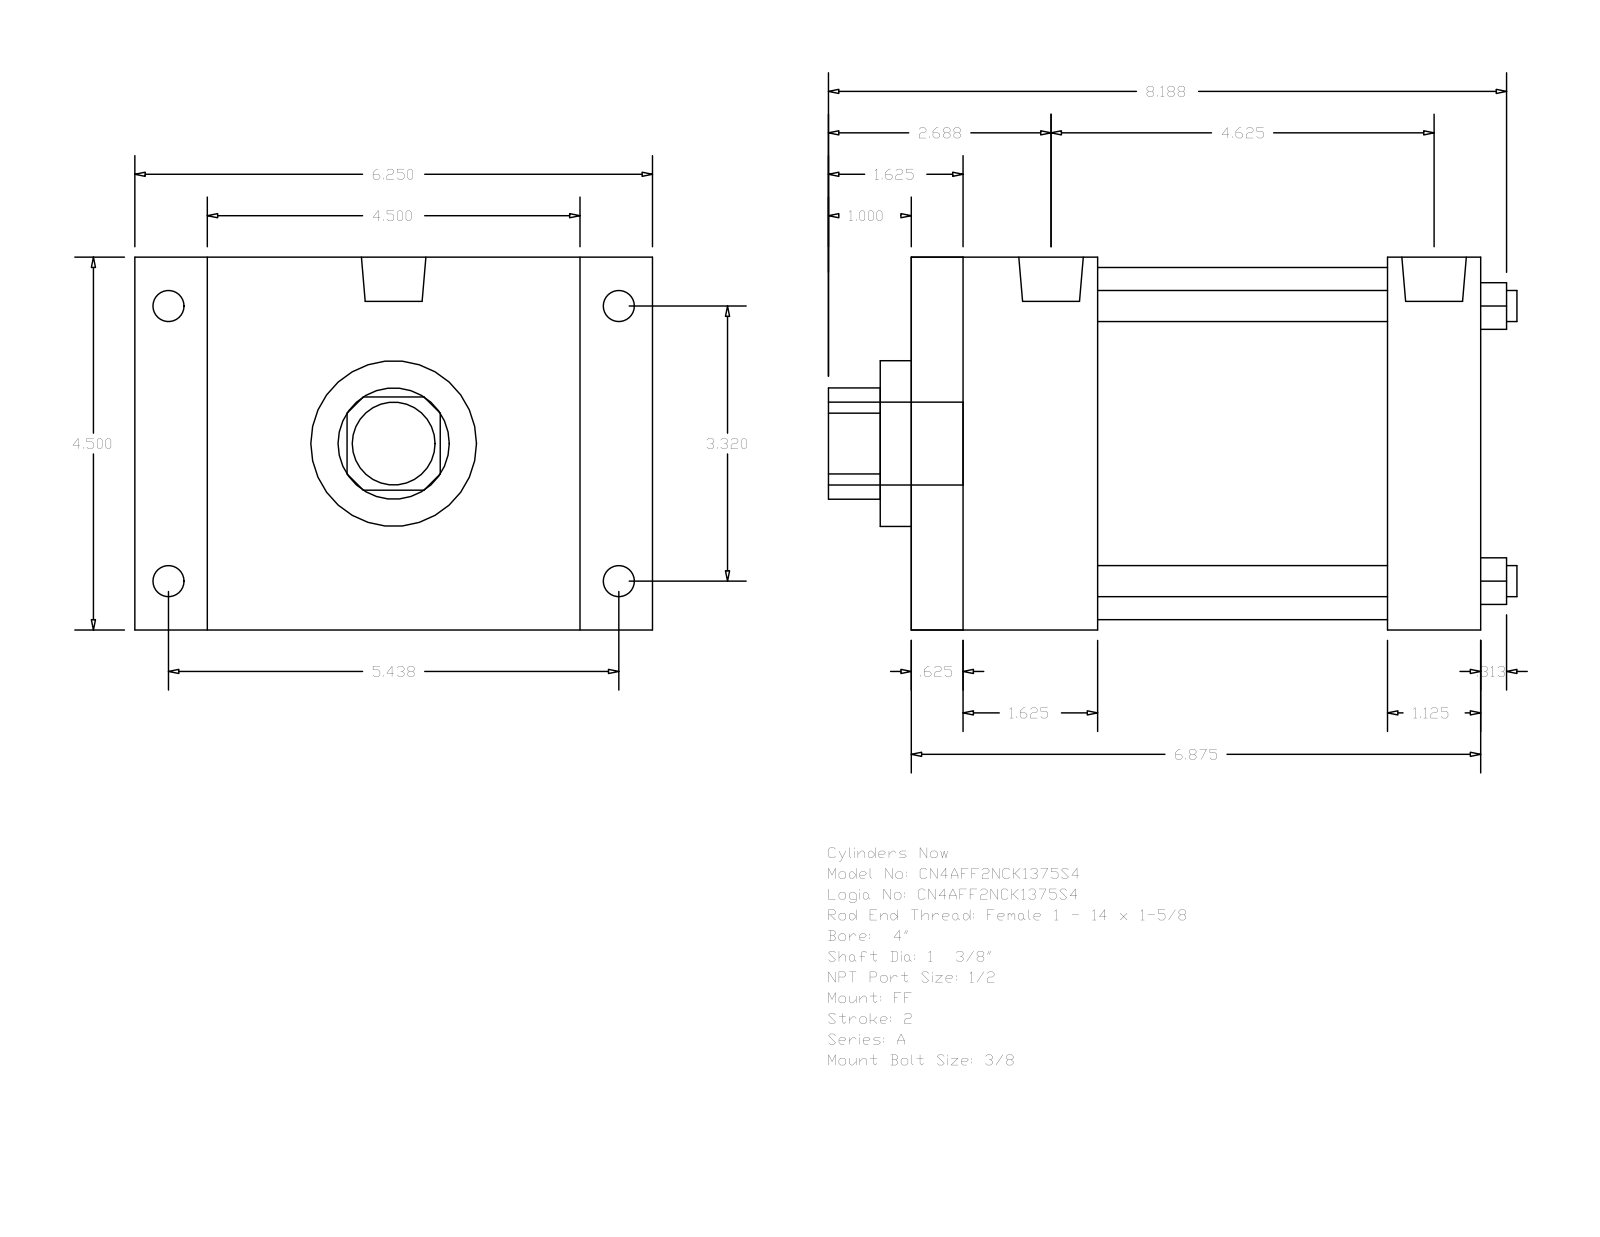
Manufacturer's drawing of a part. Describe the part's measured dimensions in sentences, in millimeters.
The part is named "A_FF__0400_1.375". Its 3-D file was written by "GSSL Pune (CONFIG_CONTROL_DESIGN)". It is 0 solids with 92 faces: 64 planar, 28 cylindrical and 0 other. Overall it measures 211.14 by 158.75 by 114.3 millimeters. Round holes: 4 of diameter 9.53, 1 of diameter 34.92, 1 of diameter 50.8, 1 of diameter 107.95. Round bosses or shafts: 4 of diameter 9.53, 4 of diameter 8.73, 2 of diameter 19.77, 1 of diameter 25.4. Partial cylindrical surfaces (rounded edges, fillets, slot ends): 1 of radius 17.06. The main face-to-face distances are 114.3, 174.63, 158.76, 15.87, 28.58, 22.23, 136.53, 146.05, 130.18, 57.15. The hole center spacings are 59.62, 84.32, 119.25.
